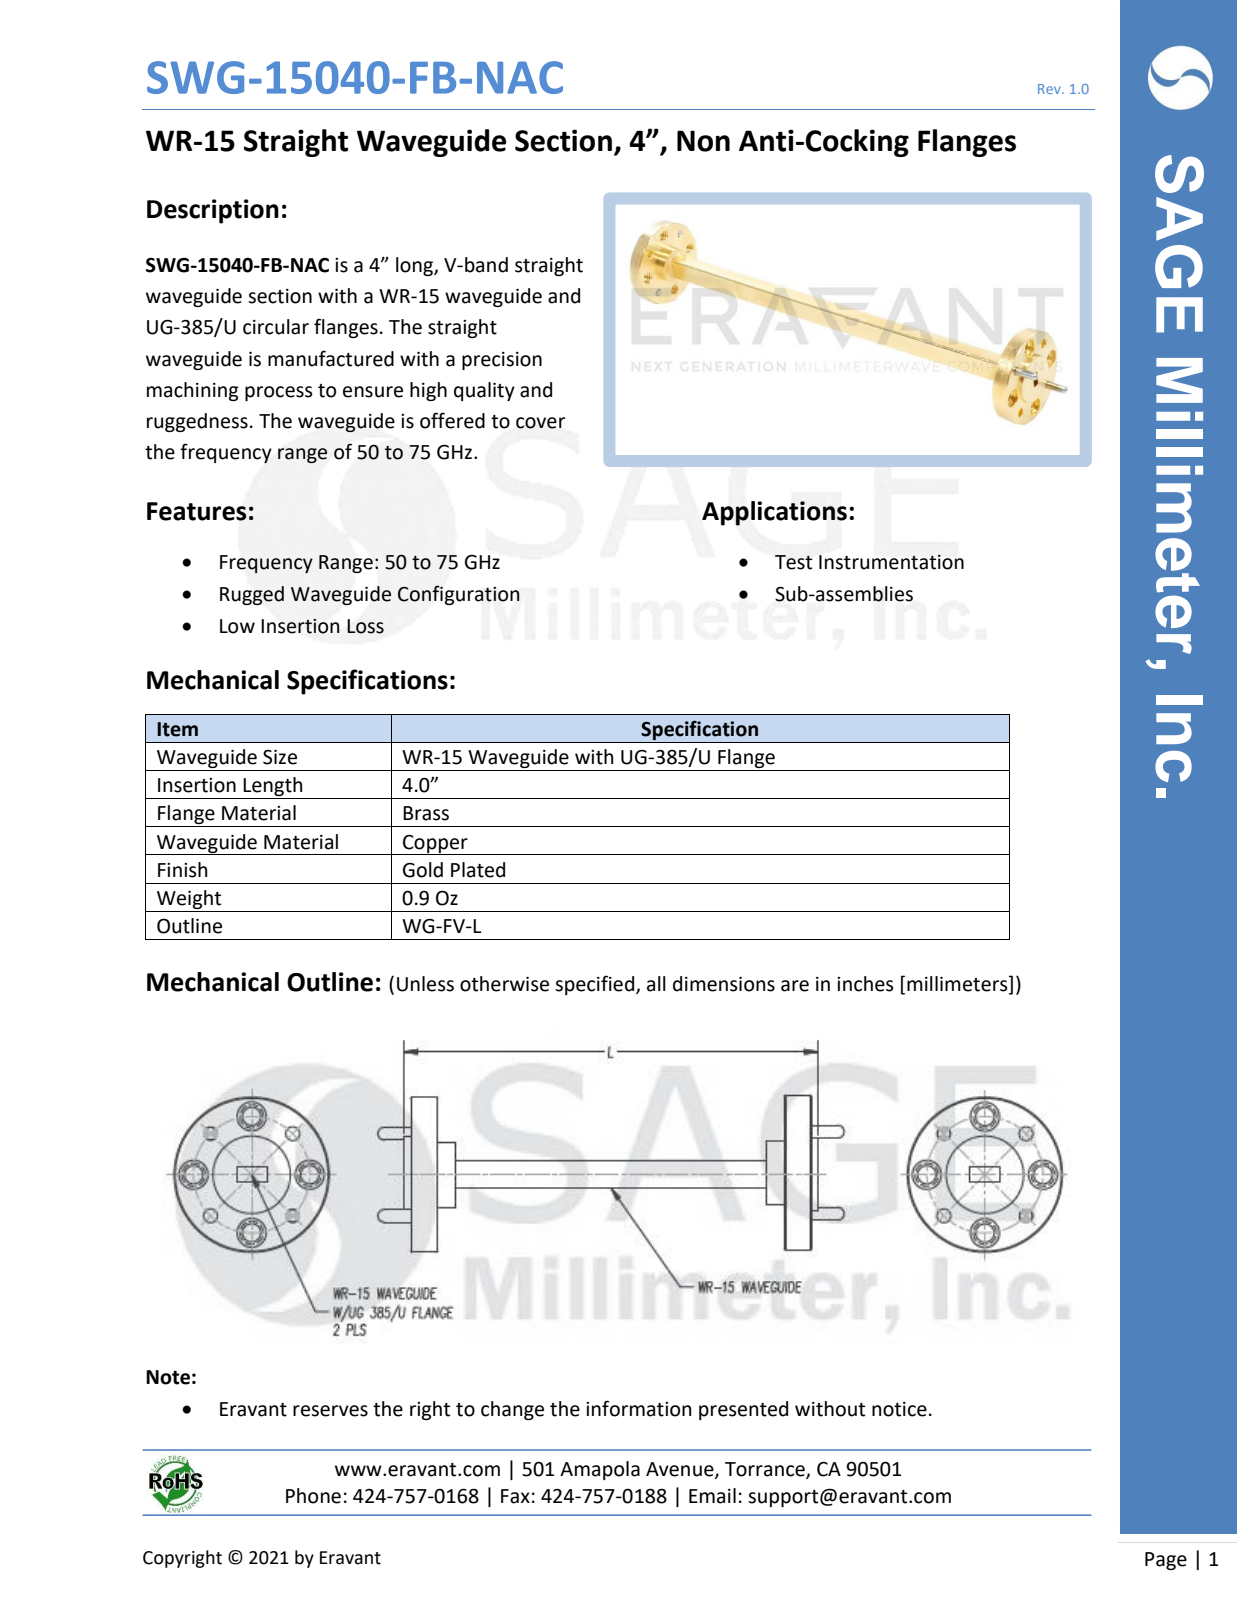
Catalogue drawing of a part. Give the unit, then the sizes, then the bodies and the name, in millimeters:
Units: millimetres
Overall size (bounding box): 109.3 × 19.1 × 19.1
Round holes (diameter × count): ⌀1.5 ×4, ⌀1.7 ×4, ⌀2.3 ×4, ⌀3.6 ×4
Round bosses / shafts (diameter × count): ⌀1.6 ×4, ⌀19.1 ×1, ⌀9.5 ×1, ⌀9.1 ×1
Main face-to-face distances: 3.9, 5.8, 3.3, 96.8, 93.5, 100.1, 0.8, 4.1, 97.5, 100.8
Hole centre spacings: 5.5, 10.1, 13.2, 14.3
Volume: 4 160 mm³ · Surface area: 3 771 mm²
Bodies: 5 solids, 146 faces (38 planar, 68 cylindrical, 40 other)
Part name (STEP PRODUCT): SWG-15040-FB
STEP written by: SolidWorks 2021 (CONFIG_CONTROL_DESIGN)
